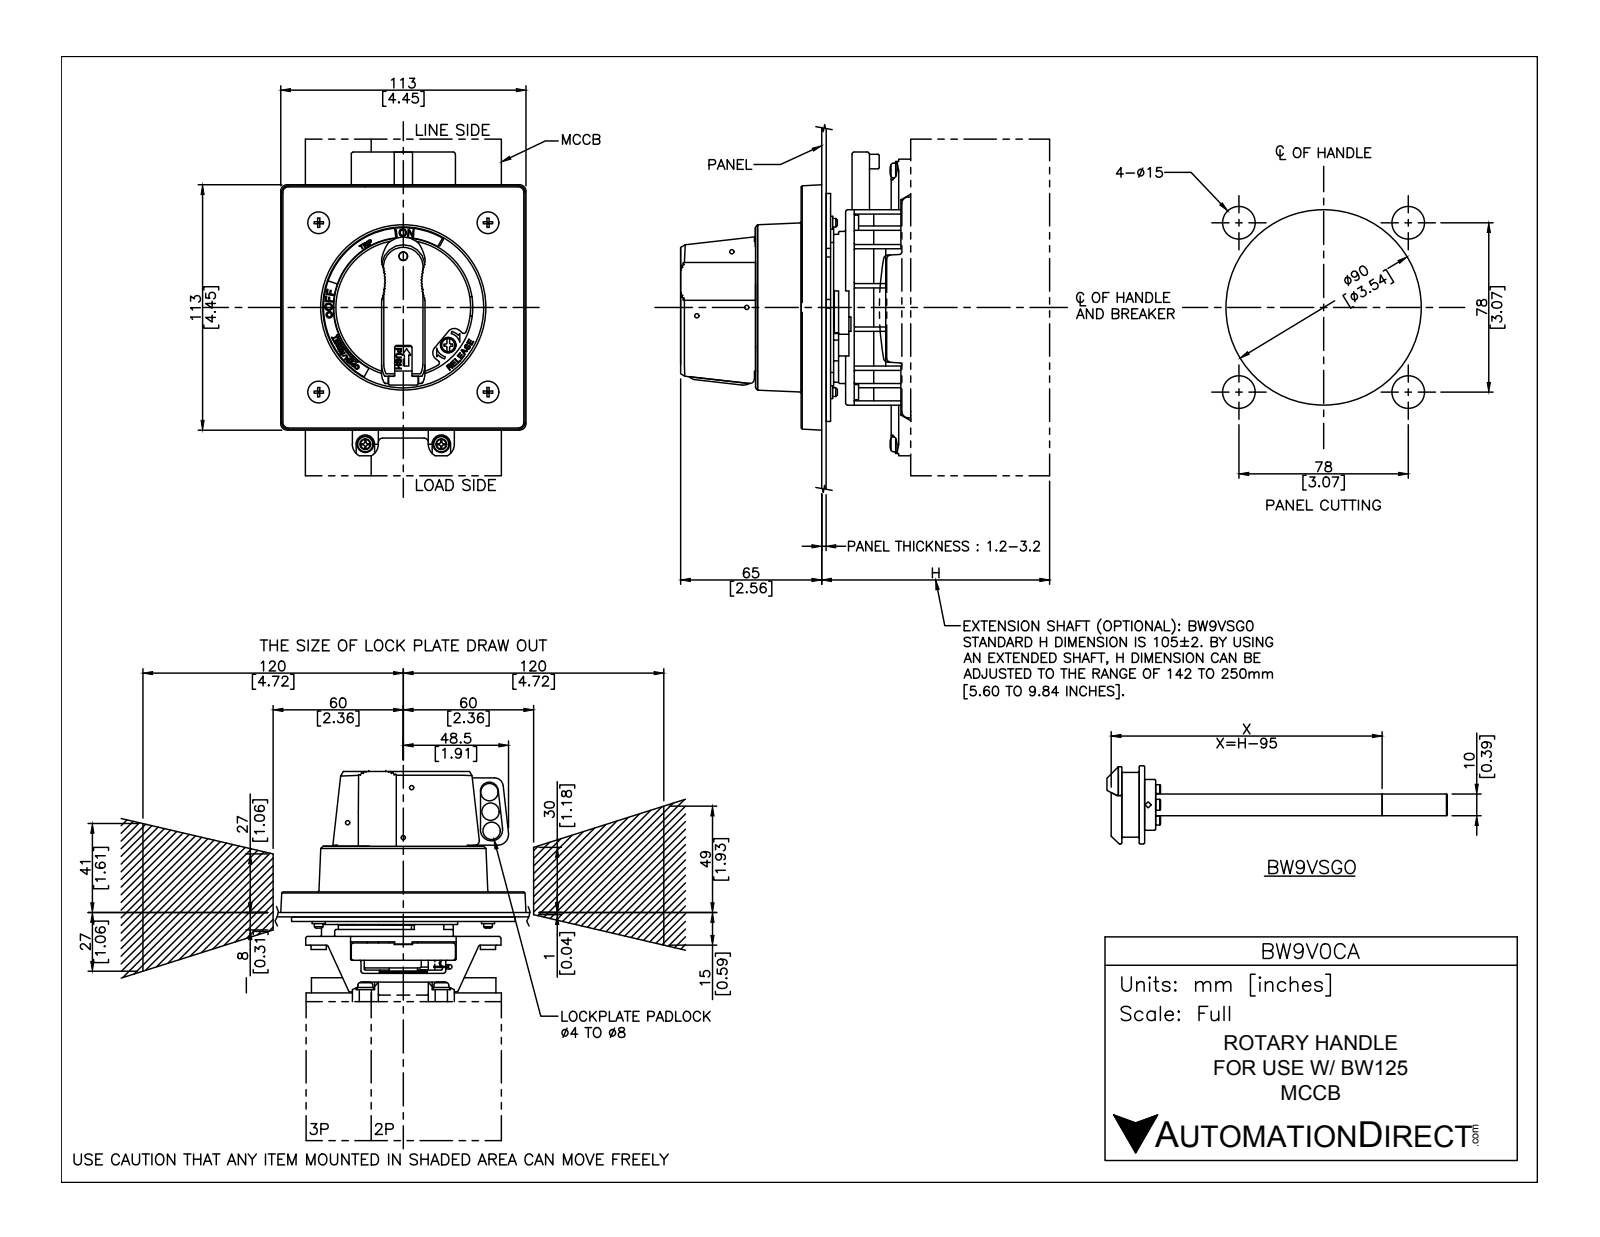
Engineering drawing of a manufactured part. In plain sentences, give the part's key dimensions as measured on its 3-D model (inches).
The part is named "BW9V0CA". Its 3-D file was written by "SolidWorks 2021 (CONFIG_CONTROL_DESIGN)". It is 20 solids with 495 faces: 254 planar, 215 cylindrical and 26 other. Overall it measures 7.276 by 5.591 by 4.449 inches. Its volume is 19.98 cubic inches and its surface area 172.6 square inches. Round holes: 4 of diameter 0.138, 4 of diameter 0.157, 4 of diameter 0.161, 4 of diameter 0.169, 4 of diameter 0.177, 4 of diameter 0.339, 1 of diameter 0.118, 1 of diameter 0.236, 1 of diameter 2.52, 1 of diameter 2.992. Round bosses or shafts: 8 of diameter 0.276, 4 of diameter 0.394, 4 of diameter 0.315, 4 of diameter 0.303, 4 of diameter 0.299, 4 of diameter 0.197, 4 of diameter 0.157, 1 of diameter 3.071. Partial cylindrical surfaces (rounded edges, fillets, slot ends): 17 of radius 0.039, 16 of radius 0.02, 12 of radius 0.118, 8 of radius 0.079, 4 of radius 0.161, 2 of radius 0.863, 1 of radius 0.012, 1 of radius 0.098. The main face-to-face distances are 0.374, 0.126, 0.079, 0.35, 0.5, 0.205, 0.579, 0.571, 0.224, 0.098. The hole center spacings are 1.422, 2.171, 2.377, 2.665, 3.071, 4.241, 4.648, 1.181.
